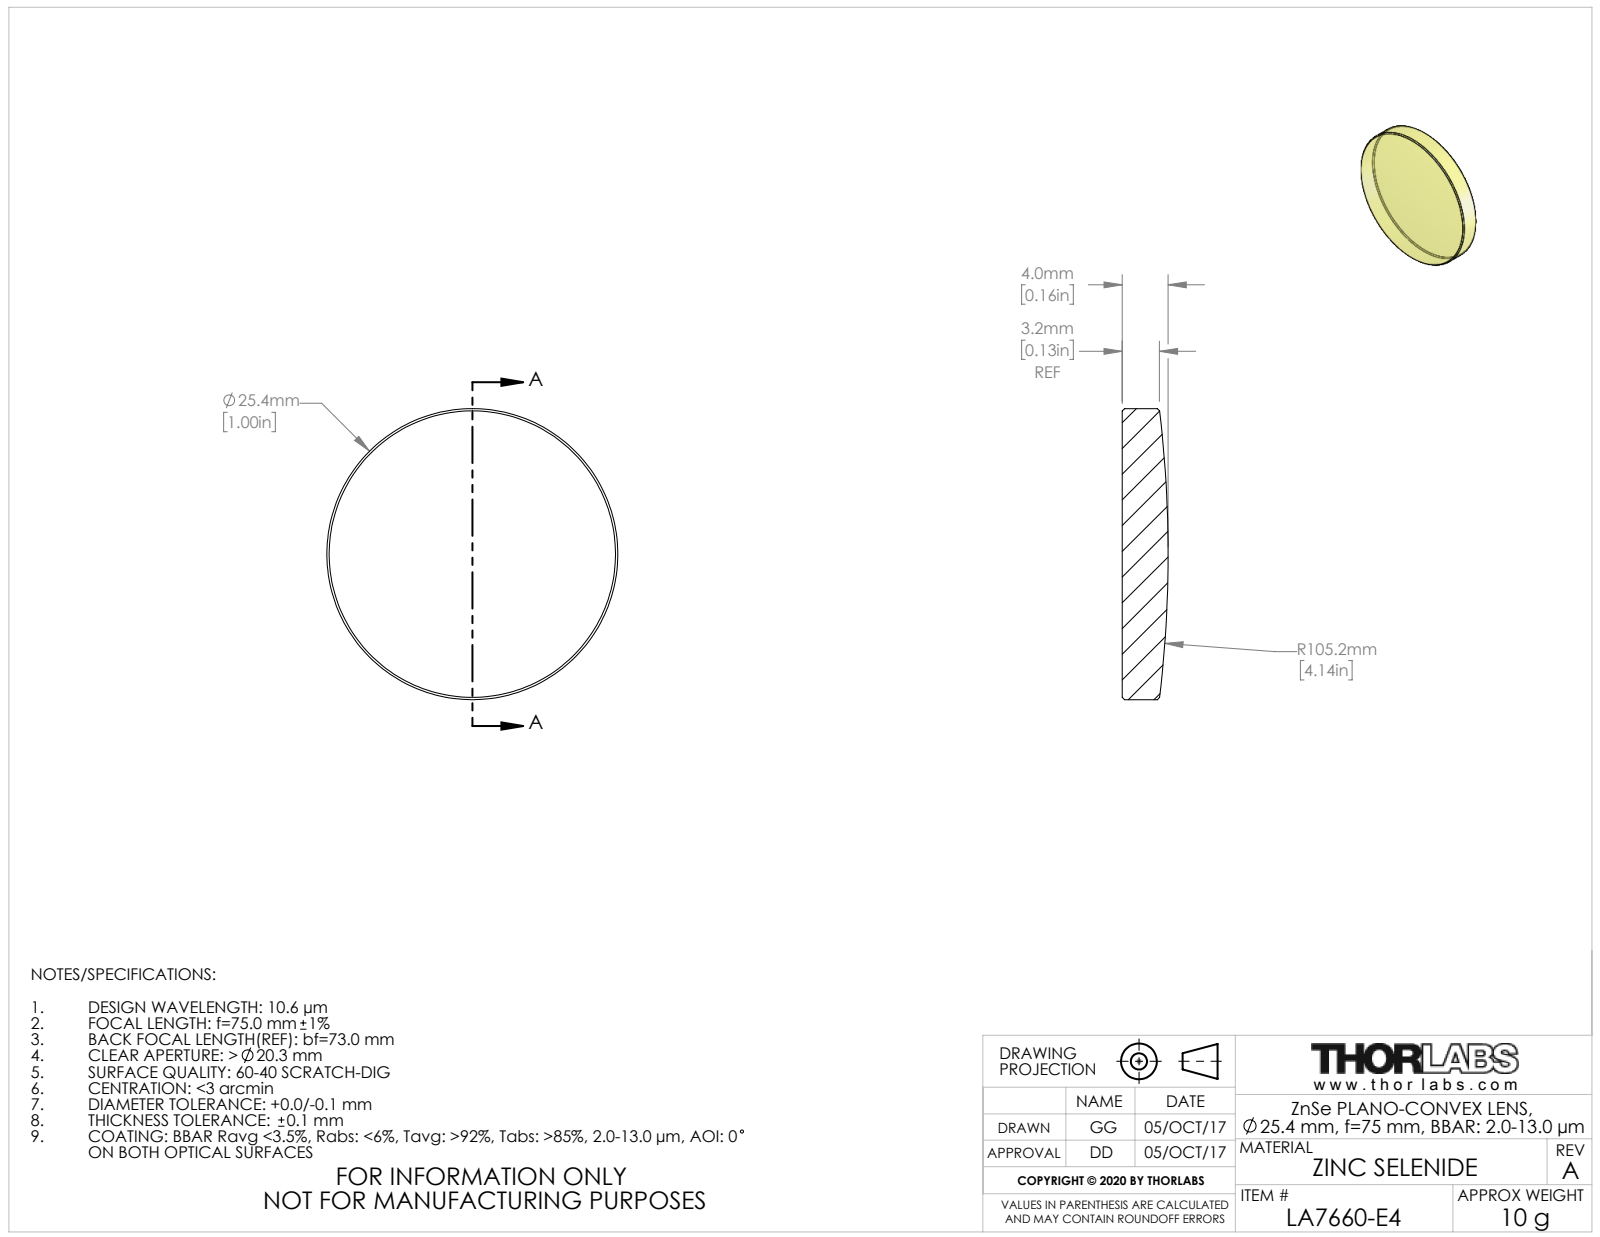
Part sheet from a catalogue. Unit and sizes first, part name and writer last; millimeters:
Units: millimetres
Overall size (bounding box): 25.4 × 25.4 × 4
Round bosses / shafts (diameter × count): ⌀25.4 ×1
Volume: 1 829 mm³ · Surface area: 1 256 mm²
Bodies: 1 solid, 9 faces (1 planar, 2 cylindrical, 6 other)
Part name (STEP PRODUCT): TTN098098-E0W
STEP written by: SolidWorks 2018 (CONFIG_CONTROL_DESIGN)
